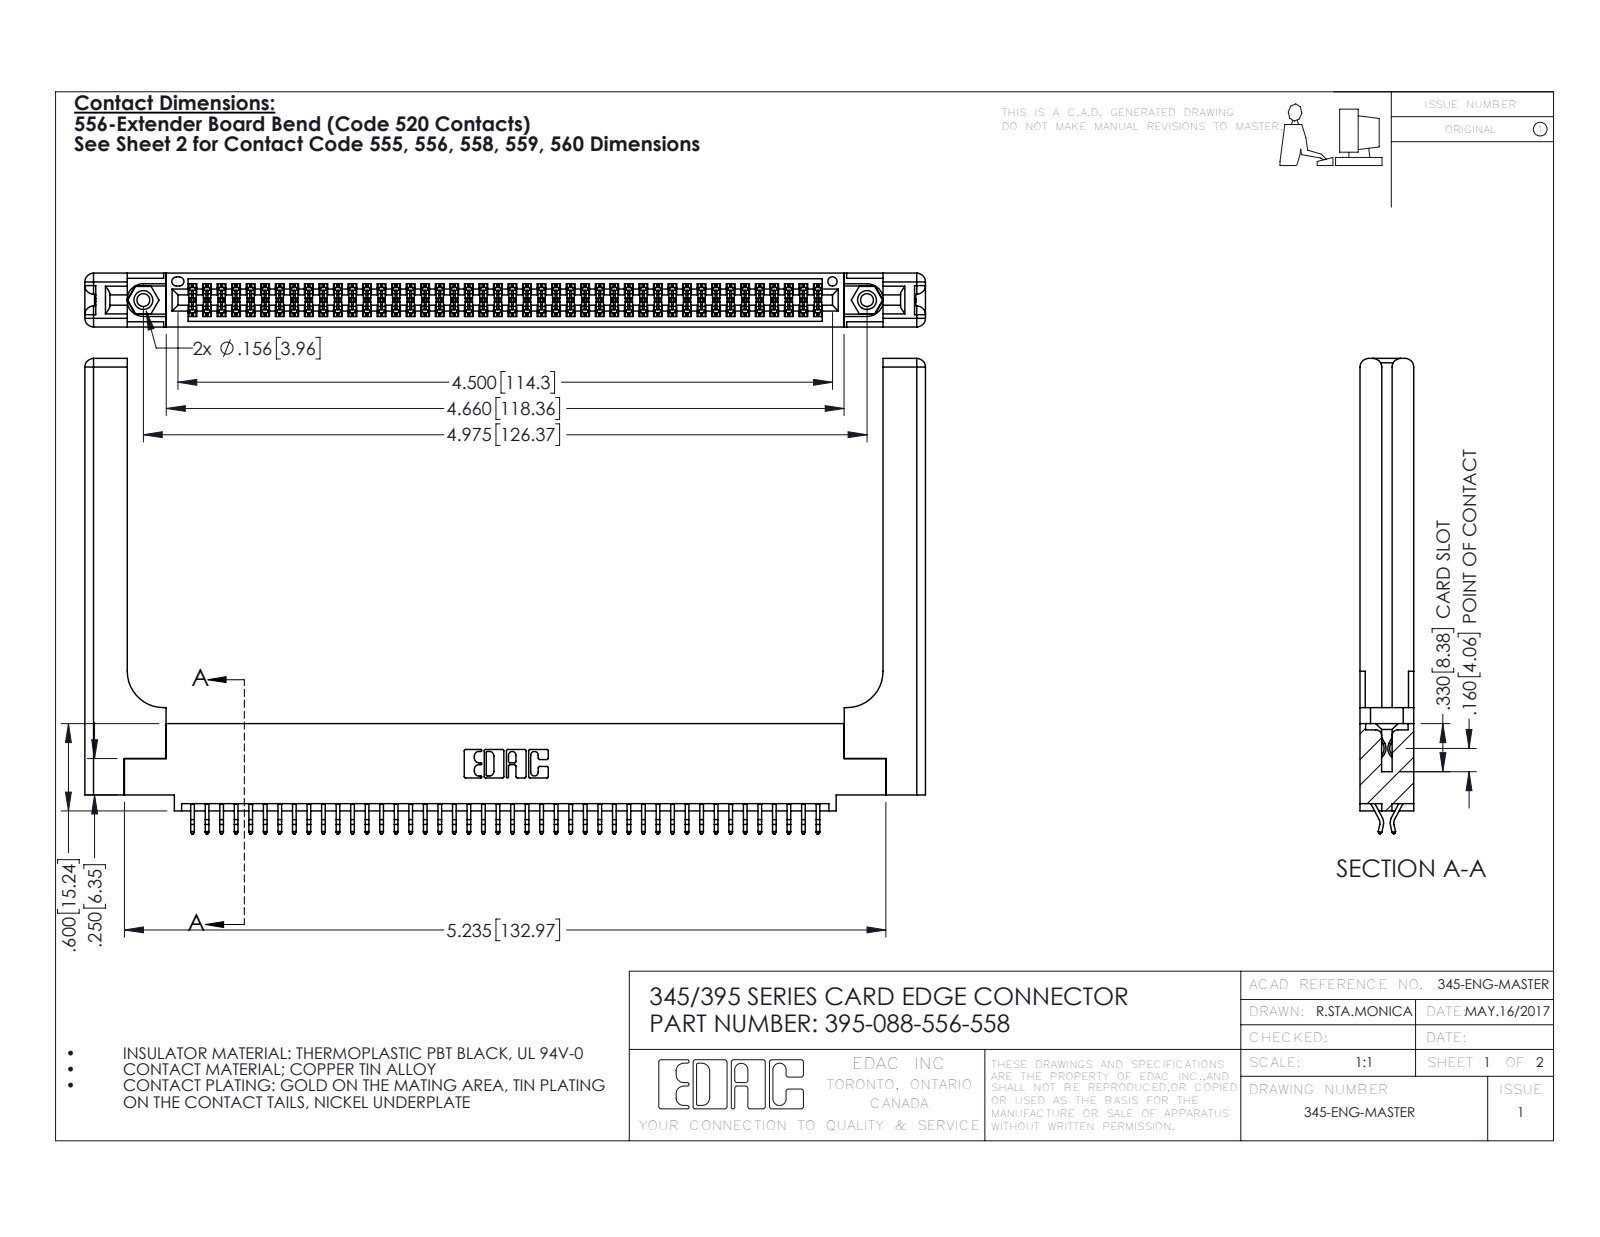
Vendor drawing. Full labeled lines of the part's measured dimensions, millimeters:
Part name (STEP PRODUCT): 345-220-058_345-220-058; 345-292-001_556 Tail; 345-250-001_345-250-001-102; 345 Part_0.110 Offset - 0.156 Dia-TH (+1 more)
STEP written by: SolidWorks 2016 (CONFIG_CONTROL_DESIGN)
Units: millimetres
Bodies: 93 solids, 5314 faces (3488 planar, 1766 cylindrical, 60 other)
Overall size (bounding box): 146.8 × 83 × 9.4
Volume: 22 680 mm³ · Surface area: 26 100 mm²
Round holes (diameter × count): ⌀2.3 ×2, ⌀3.2 ×2, ⌀4 ×2, ⌀1.6 ×1
Round bosses / shafts (diameter × count): ⌀3.9 ×2
Partial cylindrical surfaces — rounded edges, fillets, slot ends (radius × count): R0.2 ×132, R0.3 ×22, R1.5 ×16, R0.2 ×6, R0.8 ×6, R0.7 ×3, R0.3 ×2, R0.4 ×2
Main face-to-face distances: 1.8, 9.4, 7.6, 0.6, 5.1, 2.5, 6.9, 5.7, 3.8, 3.8
Hole centre spacings: 6.9, 120.4, 126.4
